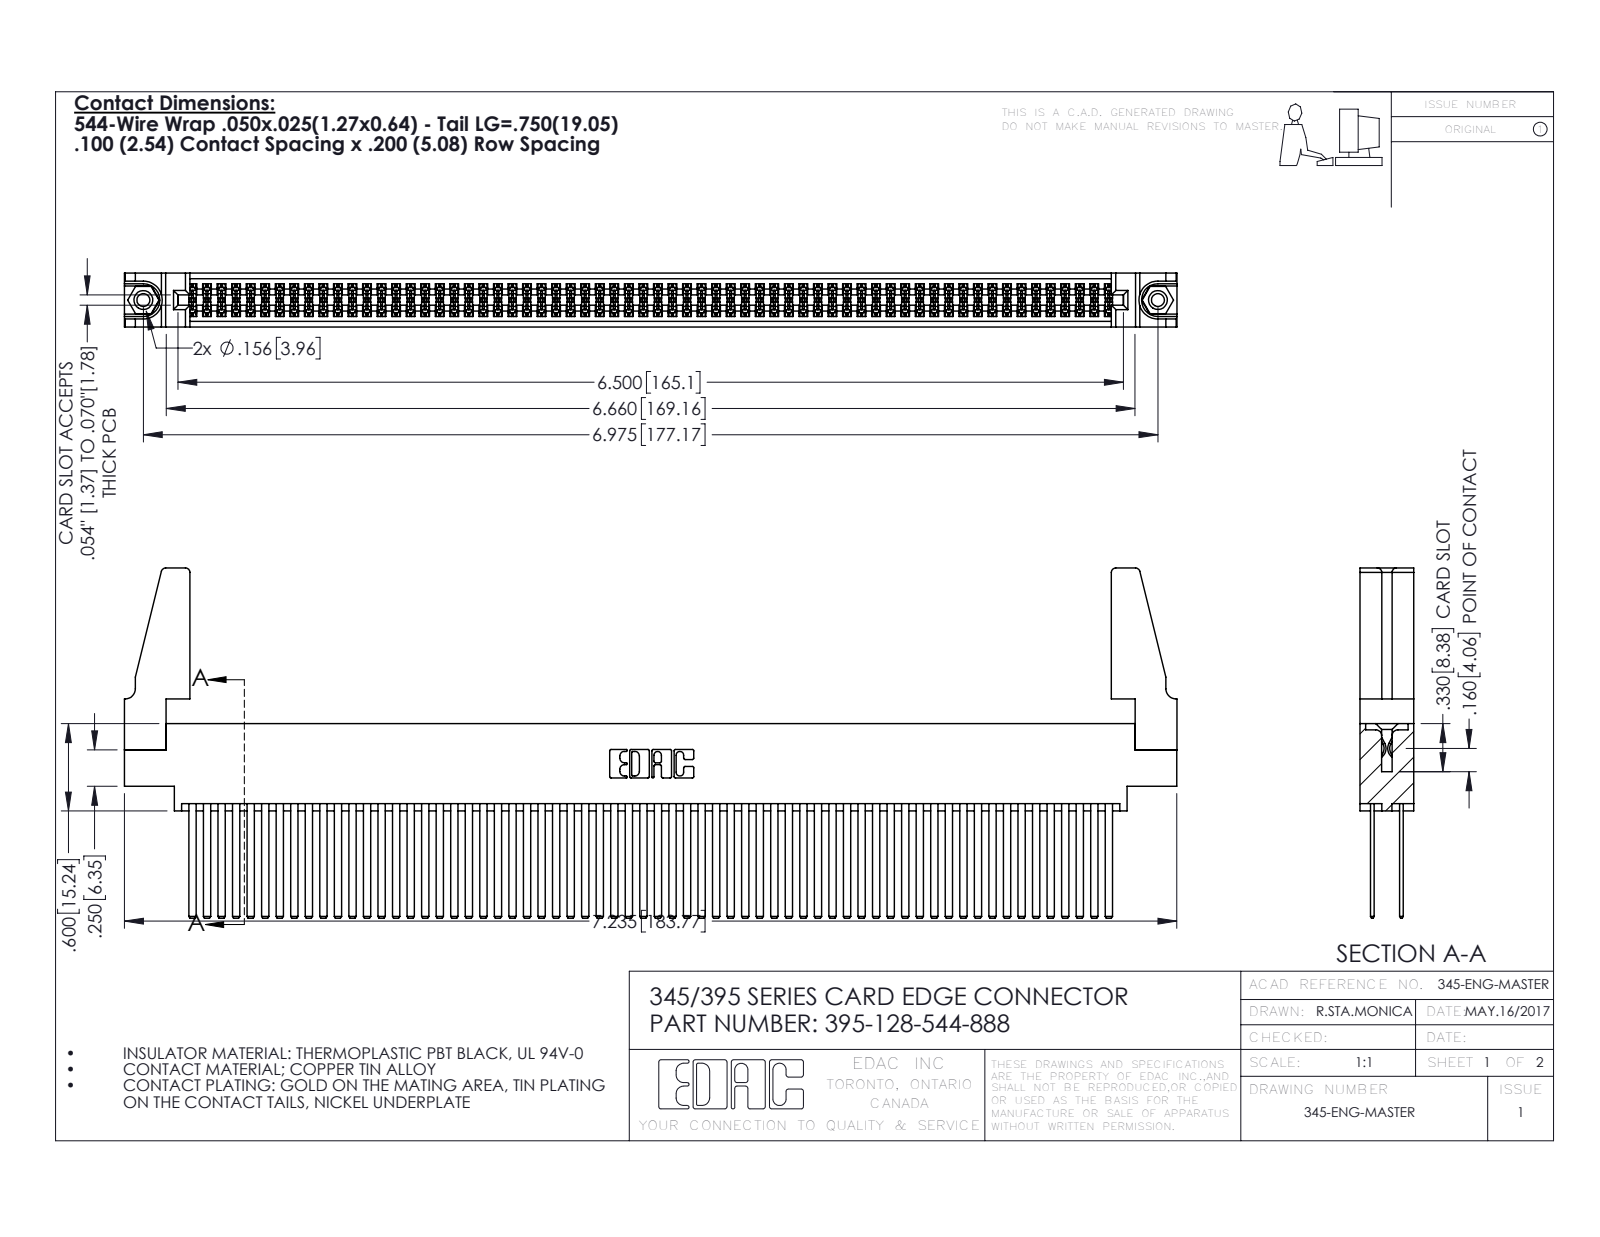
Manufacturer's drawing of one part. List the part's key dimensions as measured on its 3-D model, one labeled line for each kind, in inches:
Part name (STEP PRODUCT): 345-220-078_345-220-088; 395-128-544-888; 345 Part_0.170 Offset - 0.156 Dia-TH; 345-250-001_345-250-001-102 (+1 more)
STEP written by: SolidWorks 2016 (CONFIG_CONTROL_DESIGN)
Units: inches
Bodies: 133 solids, 5886 faces (3868 planar, 2002 cylindrical, 16 other)
Overall size (bounding box): 7.236 × 2.407 × 0.37
Volume: 1.403 in³ · Surface area: 59.1 in²
Round holes (diameter × count): ⌀0.089 ×2, ⌀0.125 ×2, ⌀0.156 ×2, ⌀0.064 ×1
Round bosses / shafts (diameter × count): ⌀0.155 ×2
Partial cylindrical surfaces — rounded edges, fillets, slot ends (radius × count): R0.006 ×192, R0.01 ×22, R0.03 ×8, R0.007 ×6, R0.031 ×6, R0.026 ×3, R0.014 ×2, R0.019 ×2
Main face-to-face distances: 0.072, 0.298, 0.2, 0.098, 0.272, 0.025, 0.225, 0.37, 0.175, 0.149
Hole centre spacings: 0.27, 6.739, 6.975
